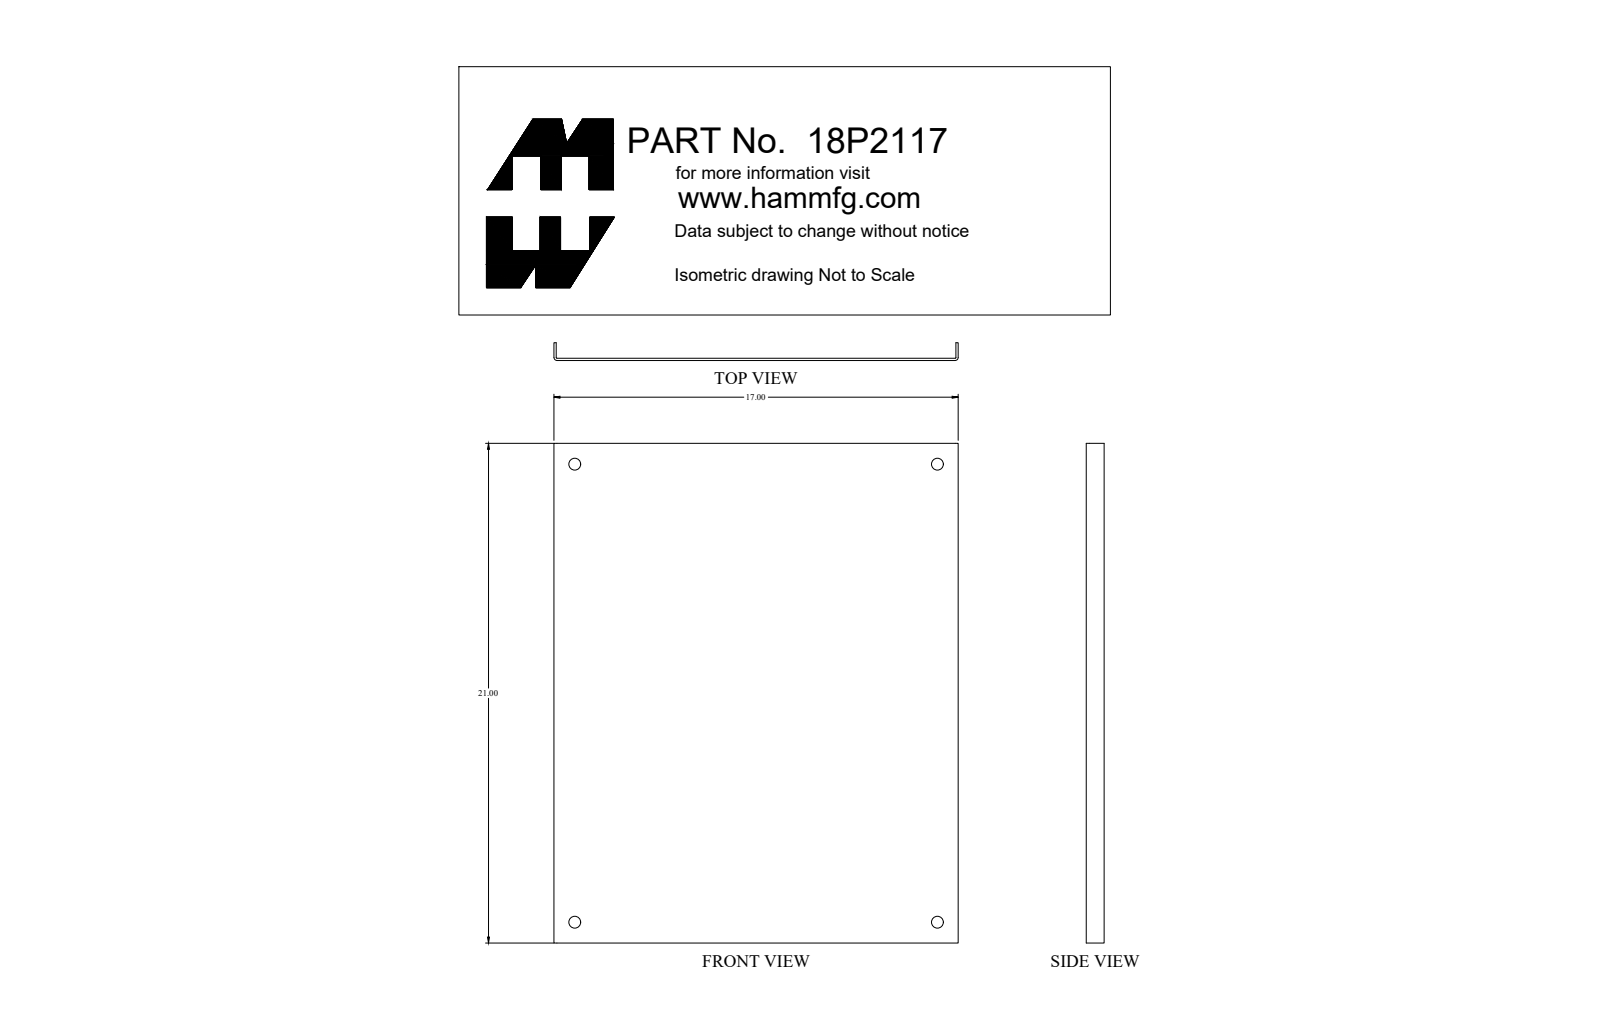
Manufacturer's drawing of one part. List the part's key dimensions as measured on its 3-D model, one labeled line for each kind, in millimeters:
Part name (STEP PRODUCT): 18P2117_Default
STEP written by: SolidWorks 2018 (CONFIG_CONTROL_DESIGN)
Units: millimetres
Bodies: 1 solid, 22 faces (10 planar, 12 cylindrical, 0 other)
Overall size (bounding box): 533.4 × 431.8 × 19.1
Volume: 595 200 mm³ · Surface area: 498 500 mm²
Round holes (diameter × count): ⌀12.7 ×4
Partial cylindrical surfaces — rounded edges, fillets, slot ends (radius × count): R0.8 ×2, R3.2 ×2
Main face-to-face distances: 2.4, 429.4, 431.8, 427, 19.1, 16.6, 533.4
Hole centre spacings: 387.4, 489, 623.8
